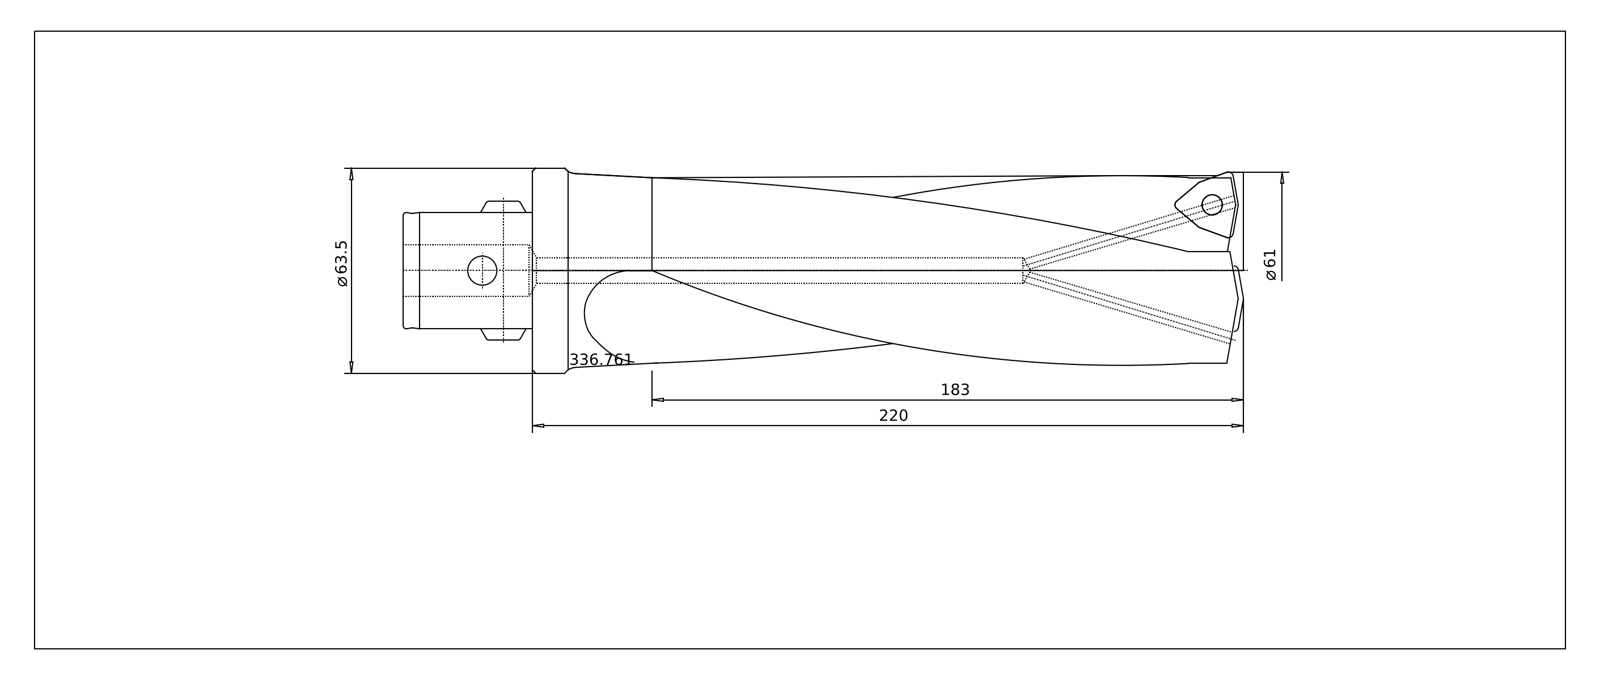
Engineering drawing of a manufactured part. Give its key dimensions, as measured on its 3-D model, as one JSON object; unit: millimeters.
{"part_name": "336.761 Kaiser WB 61-183 X CK6|694.150 Kaiser ETL M5 X 13,3 T20 IP 10S_Standard;NONE; 336.761 Kaiser WB 61-183 X CK6|336.761 Kaiser WB 61-183 X CK6_Standard-2;NONE; 336.761 Kaiser WB 61-183 X CK6|336.761 Kaiser WB 61-183 X CK6_Standard-1;NONE; 336.761 Kaiser WB 61-183 X CK6|336.761 Kaiser WB 61-183 X CK6_Standard;NONE (+2 more)", "step_written_by": "ACIS (automotive_design)", "units": "millimeters", "bodies": {"solids": 7, "faces": 354, "planar": 85, "cylindrical": 104, "other": 165}, "overall_size": [260, 63.5, 63.5], "volume_mm3": 400064, "surface_area_mm2": 65749, "round_holes": [[4.1, 2], [5, 2], [5.5, 2], [6, 1], [9, 1], [14, 1], [16, 1], [18.5, 1]], "round_bosses_or_shafts": [[7, 2], [63.5, 1], [59.48, 1], [36, 1], [13.93, 1], [10, 1]], "partial_cylinders_radius": [[0.3, 12], [0.7, 12], [0.2, 5], [2.6, 4], [1, 1], [2.29, 1]], "face_to_face_distances": [40, 5.56, 5.86, 11.42, 5.06, 5.3, 6.12, 0.56, 11.98, 51.98], "hole_center_spacings": [29.08, 227.31, 227.61, 228.04, 228.34]}
